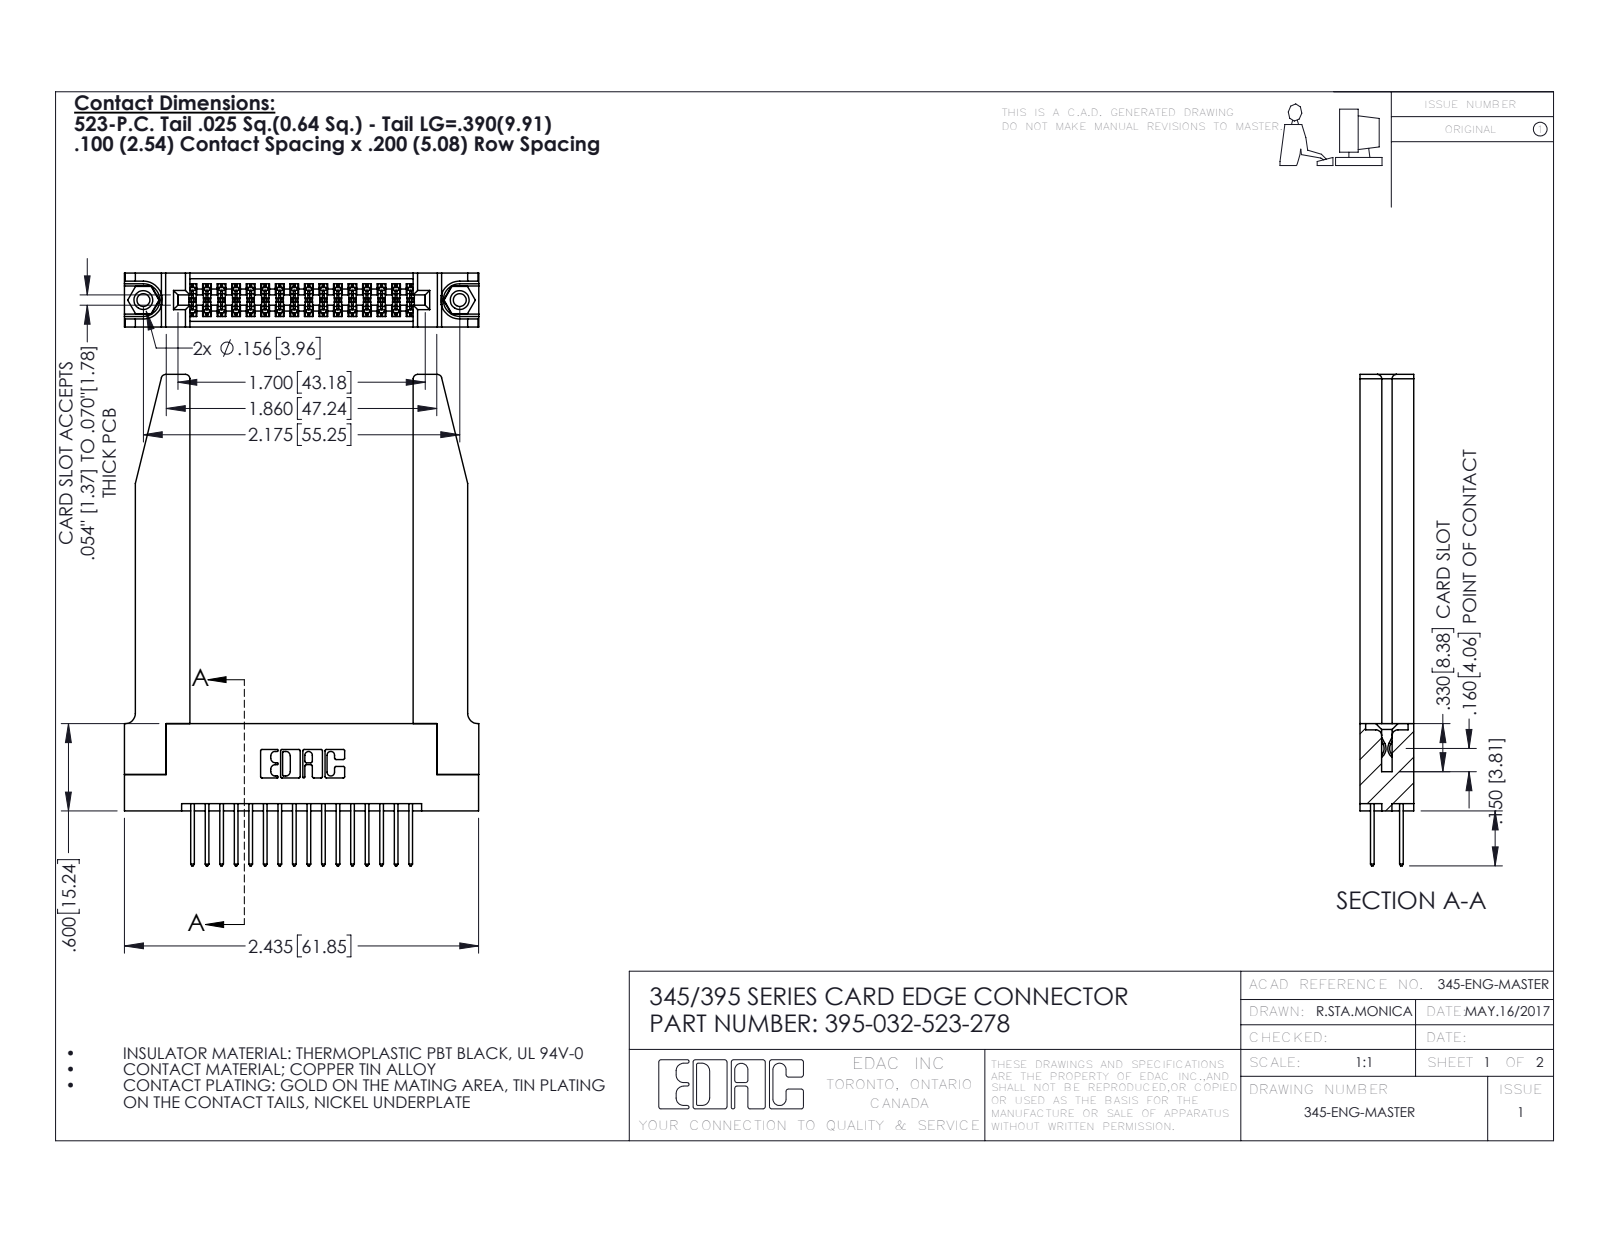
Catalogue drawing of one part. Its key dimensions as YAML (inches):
part_name: "345 Part_Flush Mounting Lugs - 0.156 Dia-TH; 345-220-078_345-220-078; 345-292-001_345-293-123; 395-032-523-278 (+1 more)"
step_written_by: "SolidWorks 2016 (CONFIG_CONTROL_DESIGN)"
units: inches
bodies: {solids: 37, faces: 1960, planar: 1278, cylindrical: 630, other: 52}
overall_size: [3.377, 2.436, 0.37]
volume: 0.83
surface_area: 23.64
round_holes:
  - {diameter: 0.089, count: 2}
  - {diameter: 0.125, count: 2}
  - {diameter: 0.156, count: 2}
  - {diameter: 0.064, count: 1}
round_bosses_or_shafts:
  - {diameter: 0.155, count: 2}
partial_cylinders:
  - {radius: 0.006, count: 48}
  - {radius: 0.01, count: 32}
  - {radius: 0.01, count: 22}
  - {radius: 0.03, count: 8}
  - {radius: 0.007, count: 6}
  - {radius: 0.031, count: 6}
  - {radius: 0.026, count: 3}
  - {radius: 0.014, count: 2}
face_to_face_distances: [0.37, 0.072, 0.298, 0.2, 0.098, 0.272, 0.025, 0.148, 0.15, 0.225]
hole_center_spacings: [0.27, 1.942, 2.175]
